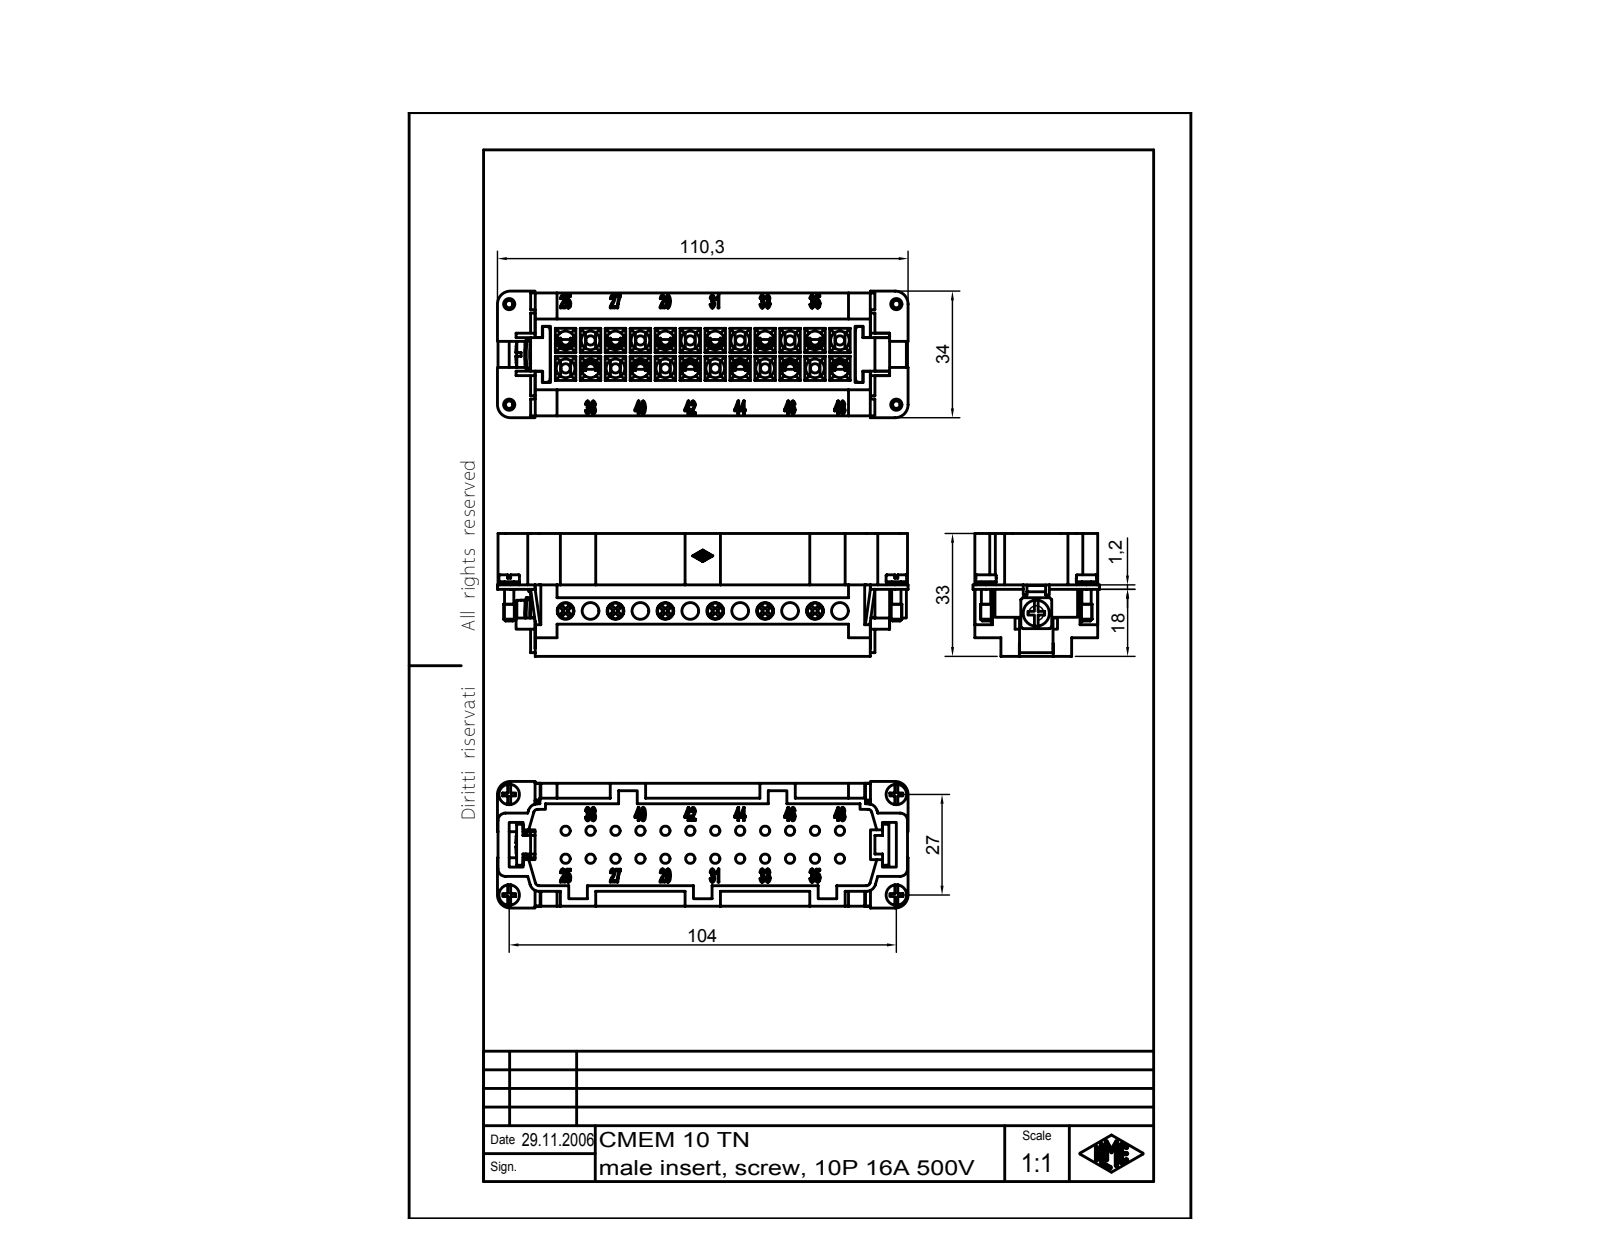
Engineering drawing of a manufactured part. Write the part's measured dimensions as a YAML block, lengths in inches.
part_name: "CMEM 10 TN"
step_written_by: "Autodesk Inventor 7 (AUTOMOTIVE_DESIGN)"
units: inches
bodies: {solids: 13, faces: 2209, planar: 1094, cylindrical: 311, other: 804}
overall_size: [4.343, 1.339, 1.299]
volume: 2.686
surface_area: 62.02
round_holes:
  - {diameter: 0.098, count: 12}
  - {diameter: 0.118, count: 12}
  - {diameter: 0.177, count: 12}
  - {diameter: 0.197, count: 12}
  - {diameter: 0.1, count: 2}
round_bosses_or_shafts:
  - {diameter: 0.165, count: 12}
  - {diameter: 0.098, count: 8}
  - {diameter: 0.217, count: 2}
  - {diameter: 0.209, count: 2}
  - {diameter: 0.118, count: 2}
  - {diameter: 0.276, count: 1}
partial_cylinders:
  - {radius: 0.004, count: 14}
  - {radius: 0.083, count: 12}
  - {radius: 0.039, count: 6}
  - {radius: 0.079, count: 6}
  - {radius: 0.098, count: 4}
  - {radius: 0.138, count: 2}
  - {radius: 0.064, count: 1}
  - {radius: 0.217, count: 1}
face_to_face_distances: [0.059, 0.866, 0.118, 0.807, 0.157, 0.276, 0.217, 1.142, 0.925, 1.024]
hole_center_spacings: [0.264, 0.528, 0.791, 1.055, 0.396, 1.319, 0.605, 0.844]
